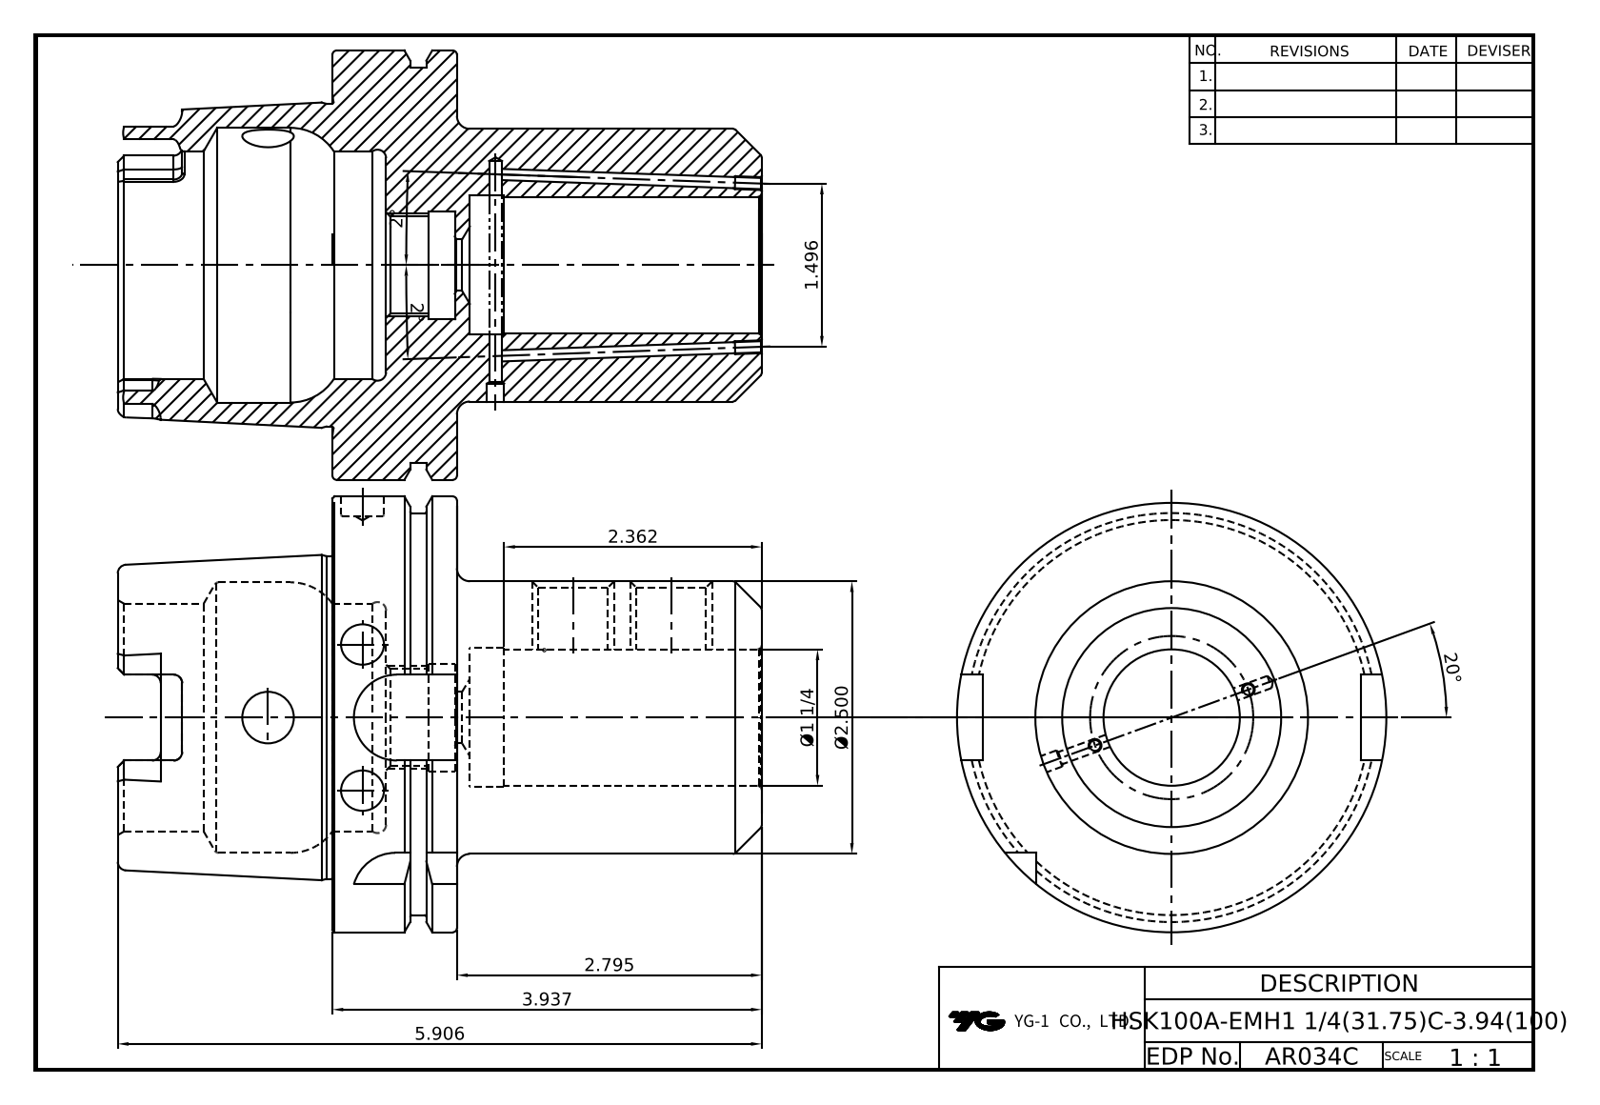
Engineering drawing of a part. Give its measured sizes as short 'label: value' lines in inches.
name: LO-HSK100A-EMH31.75C-100
written by: Autodesk Inventor 2020 (AUTOMOTIVE_DESIGN)
unit: in
bodies: 1 solid, 141 faces (42 planar, 45 cylindrical, 54 other)
size: 5.906 × 3.937 × 3.937
volume: 25.01 in³; area: 111.5 in²
holes: 3× ⌀0.394, 2× ⌀0.097, 2× ⌀0.472, 2× ⌀0.682, 1× ⌀0.118, 1× ⌀0.157, 1× ⌀0.881, 1× ⌀0.984, 1× ⌀1.25, 1× ⌀1.297, 1× ⌀2.087, 1× ⌀2.48
bosses: 1× ⌀3.937, 1× ⌀3.622, 1× ⌀2.969, 1× ⌀2.5
rounds: 6× R0.079, 4× R0.192, 4× R0.394, 1× R0.492
face distances: 1.142, 0.492, 0.65, 3.937, 3.445, 2.795, 2.461, 1.969, 3.11, 5.906
hole spacings: 1.22, 0.979, 1.852, 2.831
